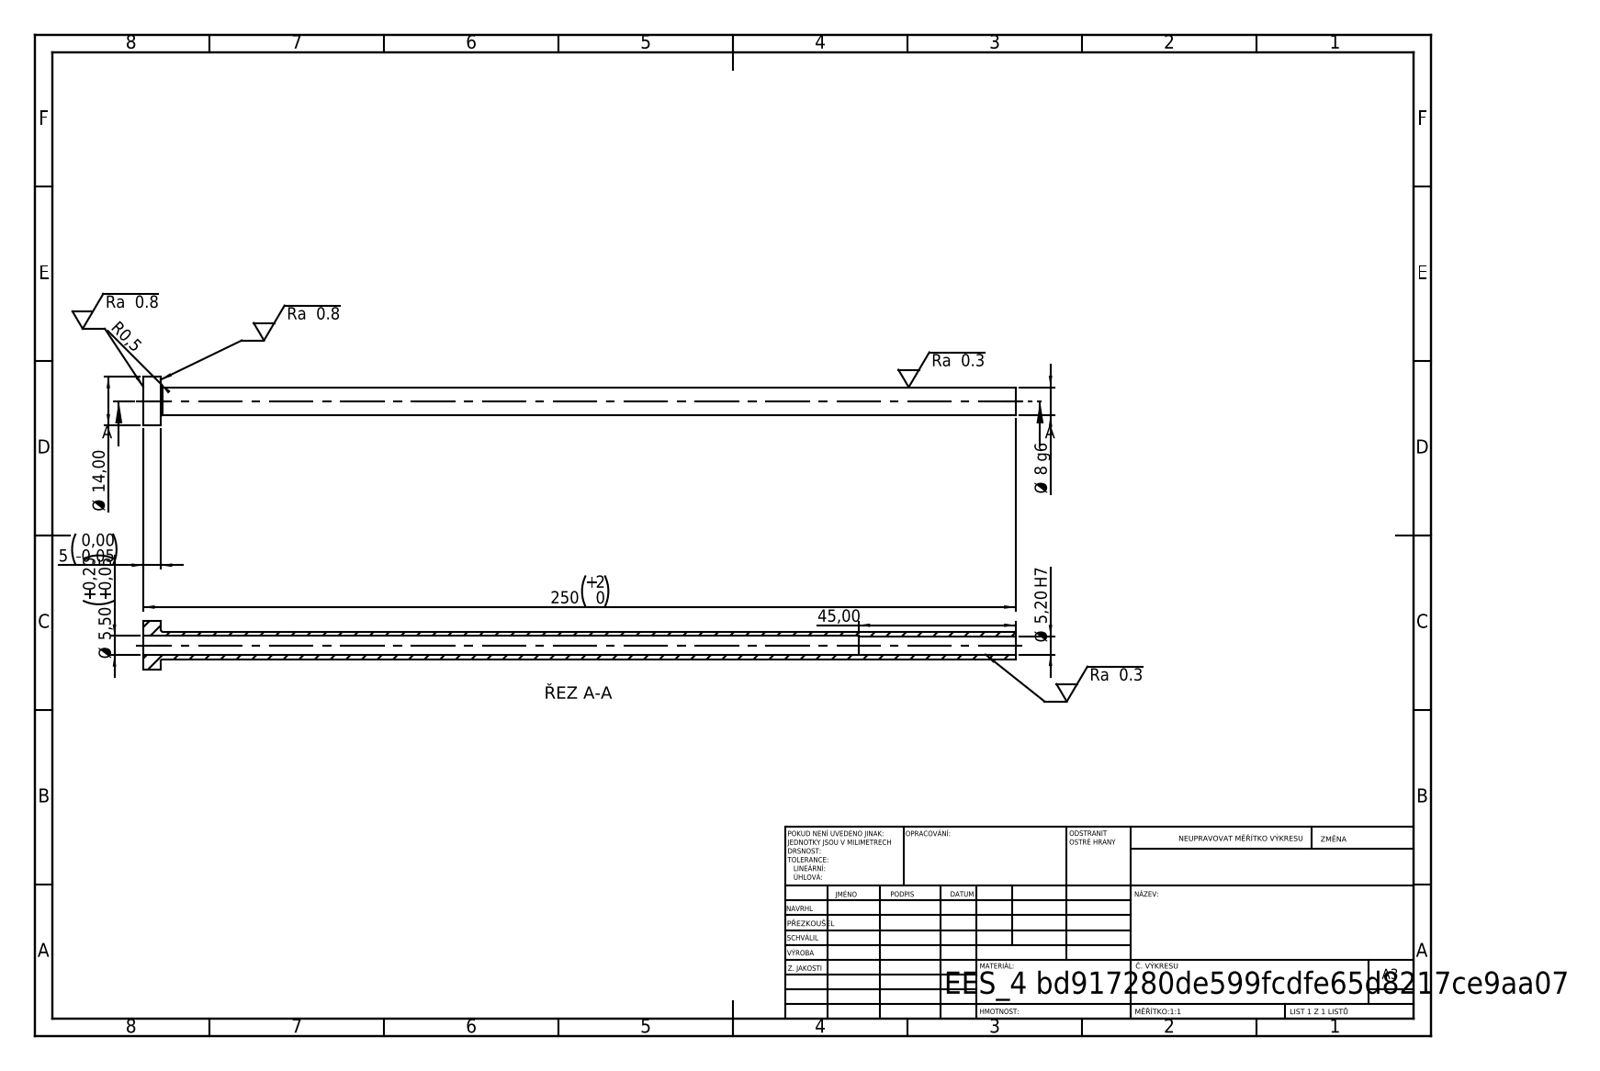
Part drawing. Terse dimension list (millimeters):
written by: SolidWorks 2019 (CONFIG_CONTROL_DESIGN)
unit: mm
bodies: 1 solid, 14 faces (4 planar, 8 cylindrical, 2 other)
size: 250 × 14 × 14
volume: 7 260 mm³; area: 10 915 mm²
holes: 1× ⌀5.2, 1× ⌀5.5
bosses: 1× ⌀14, 1× ⌀8
face distances: 5, 250, 245, 205, 200, 45
